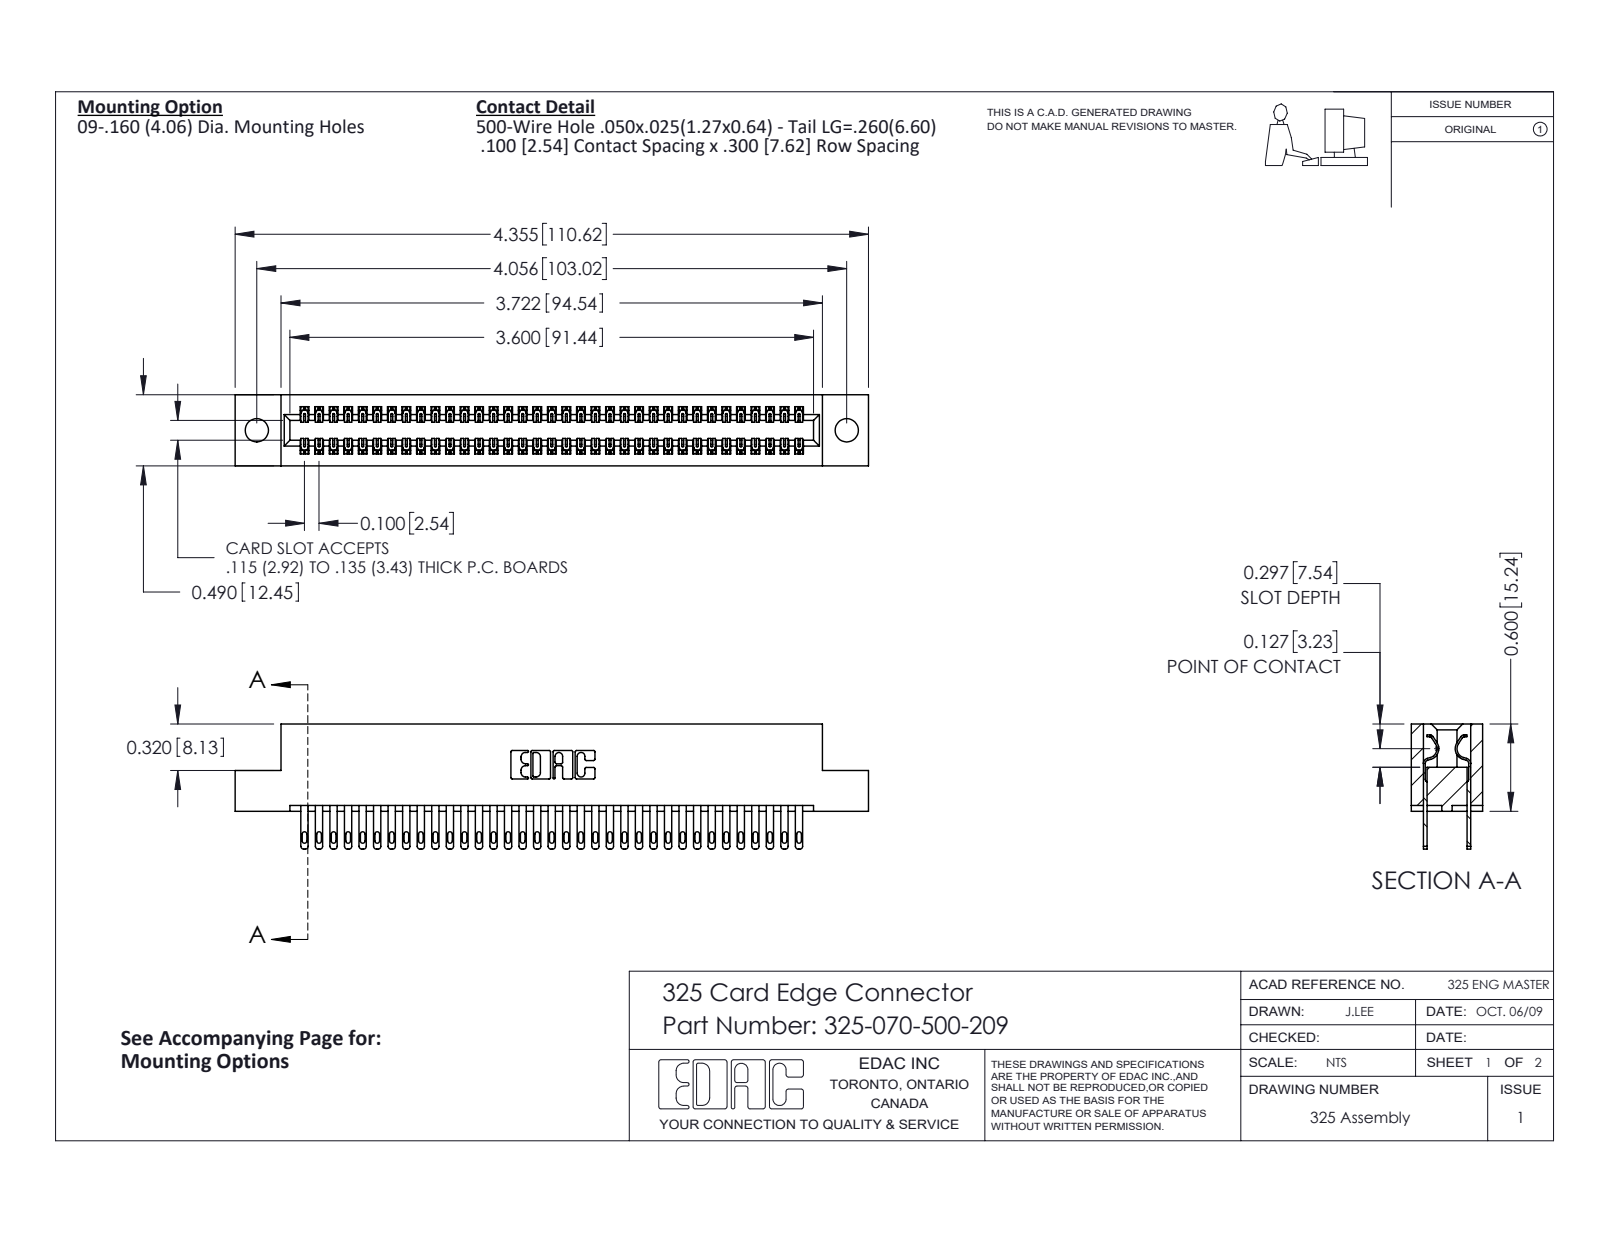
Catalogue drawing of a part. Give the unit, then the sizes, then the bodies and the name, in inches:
Units: inches
Overall size (bounding box): 4.355 × 0.86 × 0.49
Round holes (diameter × count): ⌀0.16 ×2
Partial cylindrical surfaces — rounded edges, fillets, slot ends (radius × count): R0.006 ×105, R0.016 ×70, R0.02 ×70, R0.01 ×22, R0.007 ×6, R0.031 ×6, R0.026 ×3, R0.014 ×2
Main face-to-face distances: 0.083, 0.407, 0.3, 0.107, 0.383, 0.025, 0.49, 0.325, 0.275, 0.56
Hole centre spacings: 4.056
Volume: 0.867 in³ · Surface area: 27.39 in²
Bodies: 71 solids, 3474 faces (2170 planar, 1304 cylindrical, 0 other)
Part name (STEP PRODUCT): 325 Part_.160 TH; 325-292-001_325-293-100; 325-070-500-209
STEP written by: SolidWorks 2016 (CONFIG_CONTROL_DESIGN)
